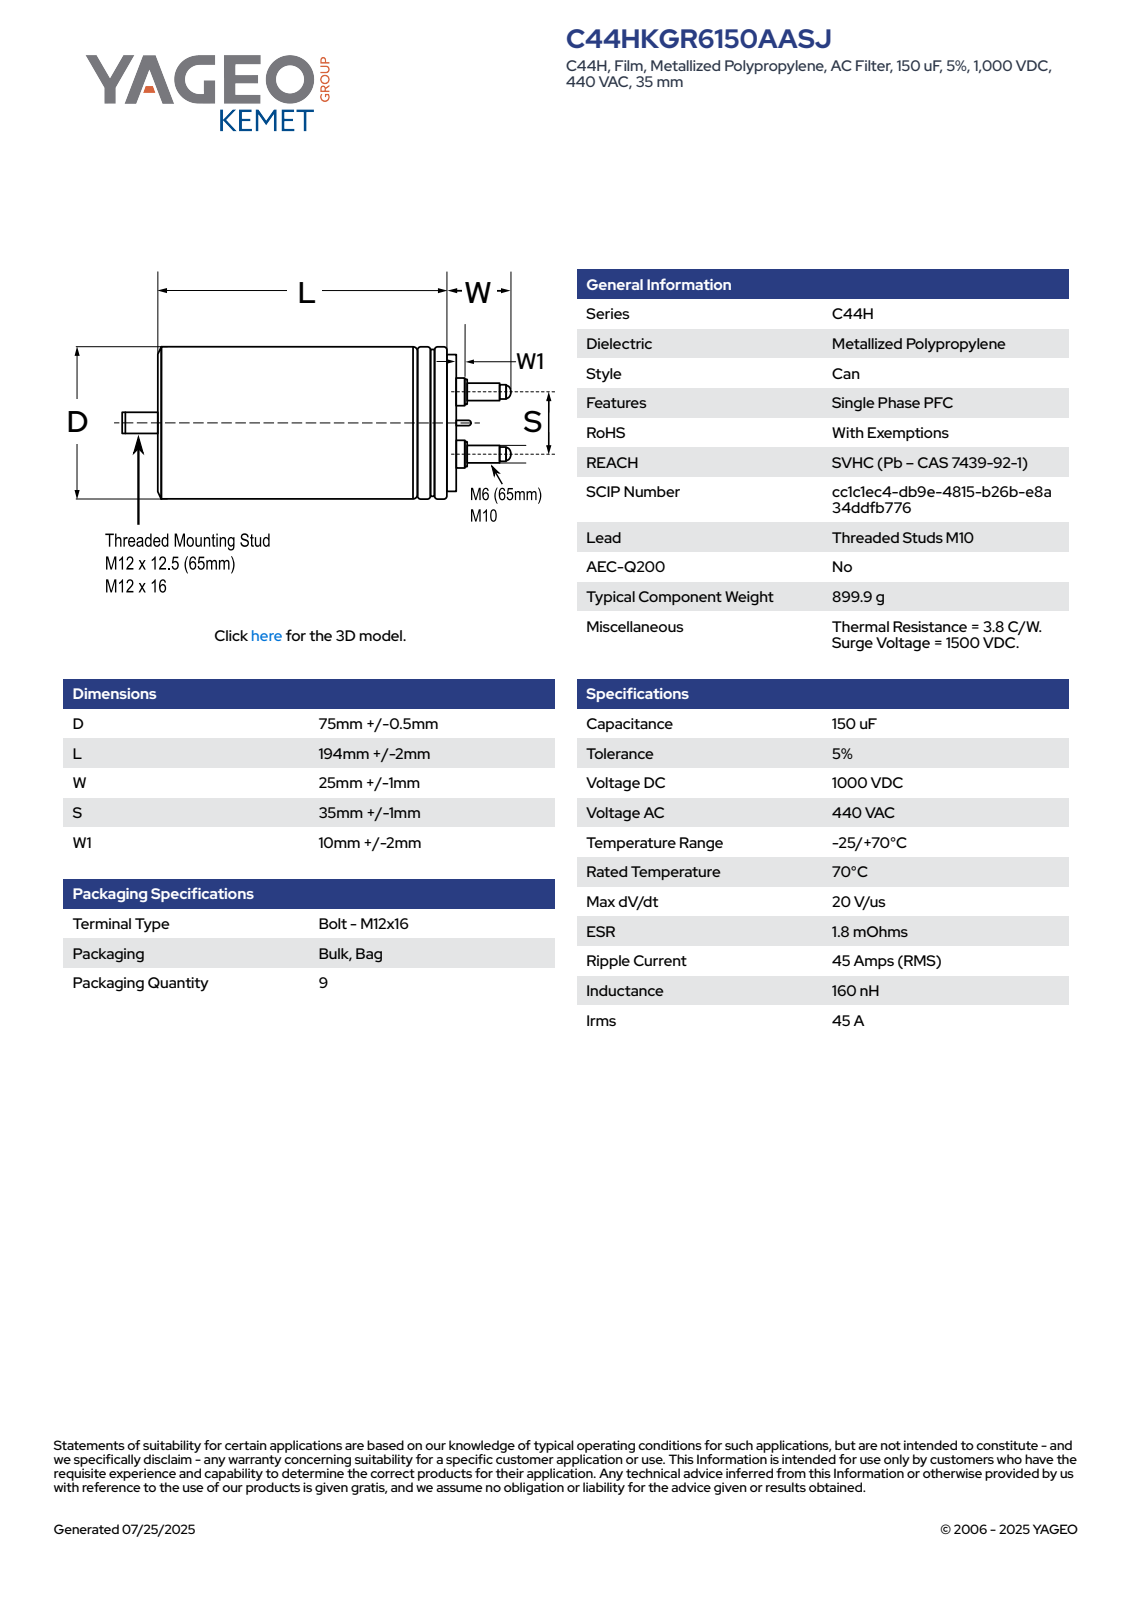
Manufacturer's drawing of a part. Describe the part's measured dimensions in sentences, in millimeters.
The part is named "CFP_C44H_75X194D75.5L196S35". Its 3-D file was written by "SolidWorks 2014 (AUTOMOTIVE_DESIGN)". It is 1 solid with 106 faces: 38 planar, 29 cylindrical and 39 other. Overall it measures 250 by 75.51 by 75.5 millimeters. Its volume is 888 585 cubic millimeters and its surface area 61 117 square millimeters. Round holes: 1 of diameter 60.23. Round bosses or shafts: 3 of diameter 12, 2 of diameter 10, 2 of diameter 9.25, 1 of diameter 75.5, 1 of diameter 64.62. Partial cylindrical surfaces (rounded edges, fillets, slot ends): 1 of radius 37.76. The main face-to-face distances are 196, 6, 202, 1.84, 208, 12, 16, 212, 218, 224.
